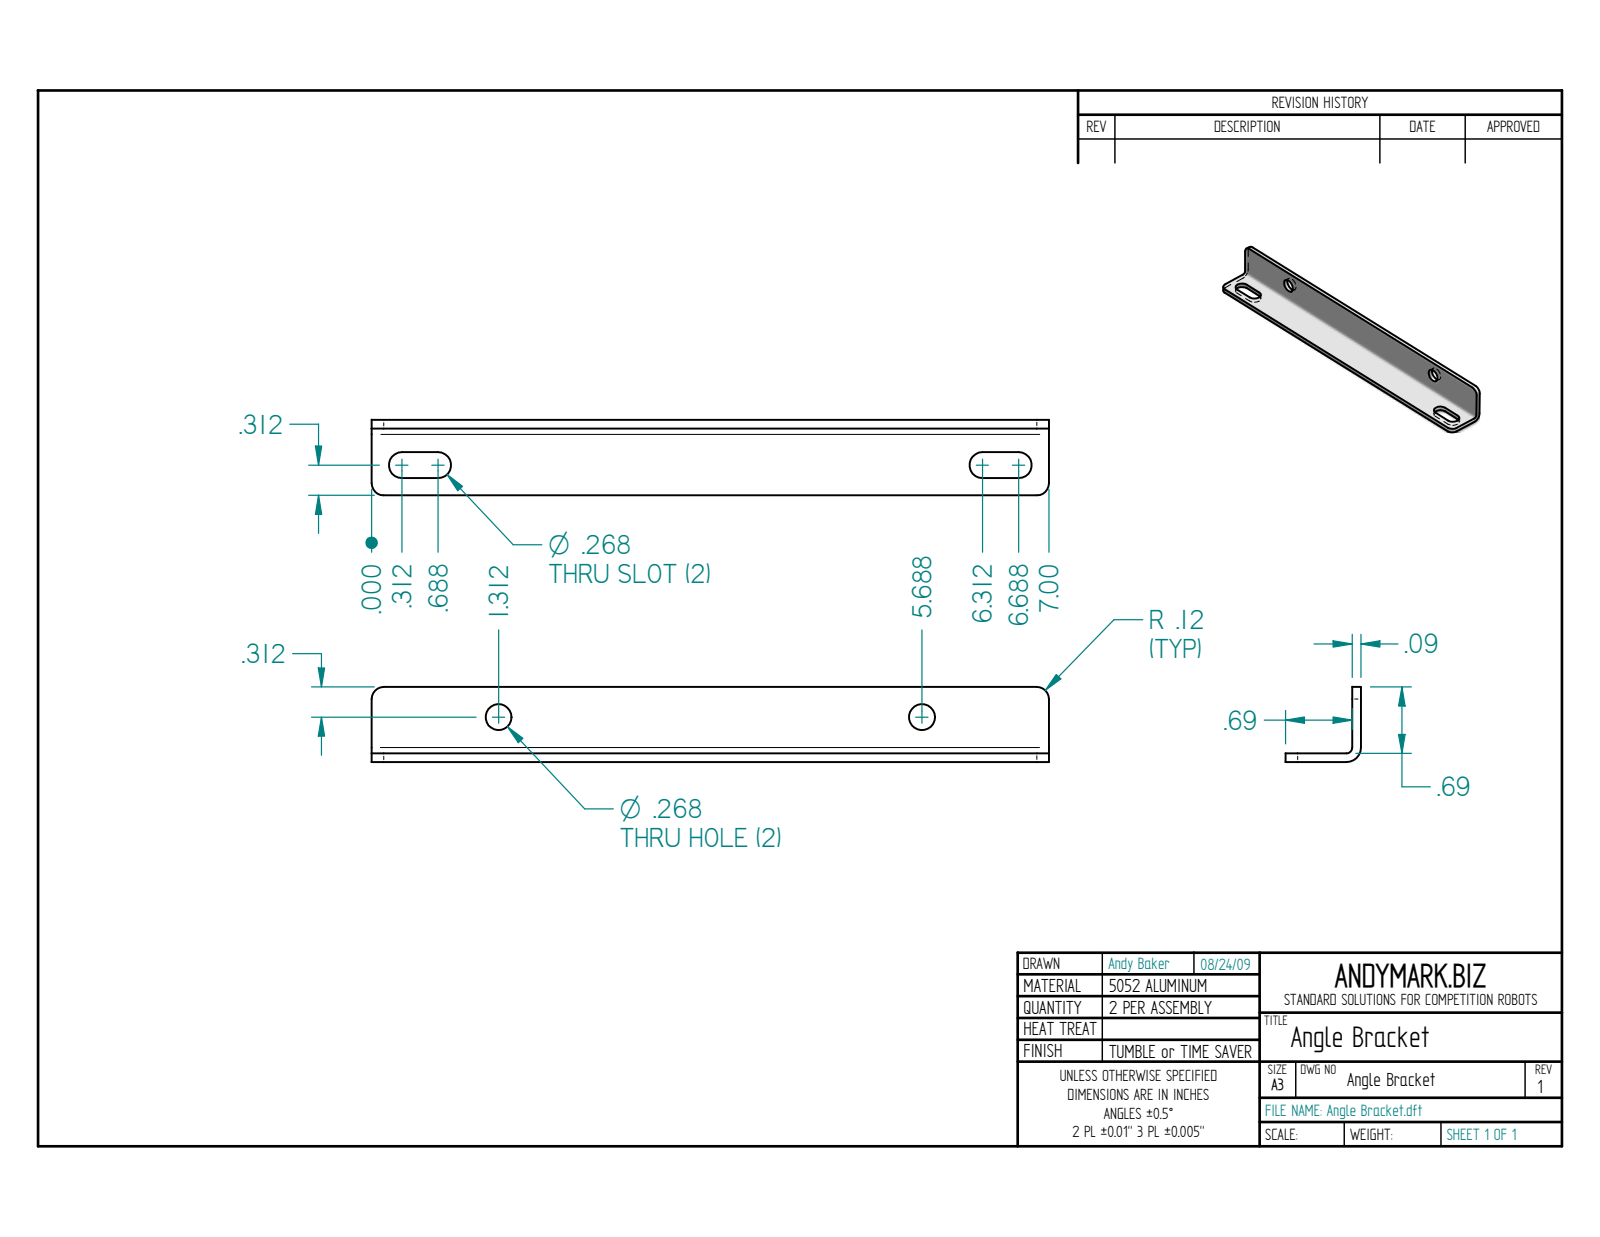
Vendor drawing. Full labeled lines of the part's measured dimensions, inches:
STEP written by: Unknown (CONFIG_CONTROL_DESIGN)
Units: inches
Bodies: 1 solid, 24 faces (12 planar, 12 cylindrical, 0 other)
Overall size (bounding box): 7 × 0.779 × 0.777
Volume: 0.856 in³ · Surface area: 20.95 in²
Round holes (diameter × count): ⌀0.268 ×2
Partial cylindrical surfaces — rounded edges, fillets, slot ends (radius × count): R0.125 ×4, R0.134 ×4, R0.06 ×1, R0.15 ×1
Main face-to-face distances: 0.09, 0.777, 0.687, 0.689, 0.779, 7, 0.179, 0.446, 0.268, 0.51
Hole centre spacings: 4.375
